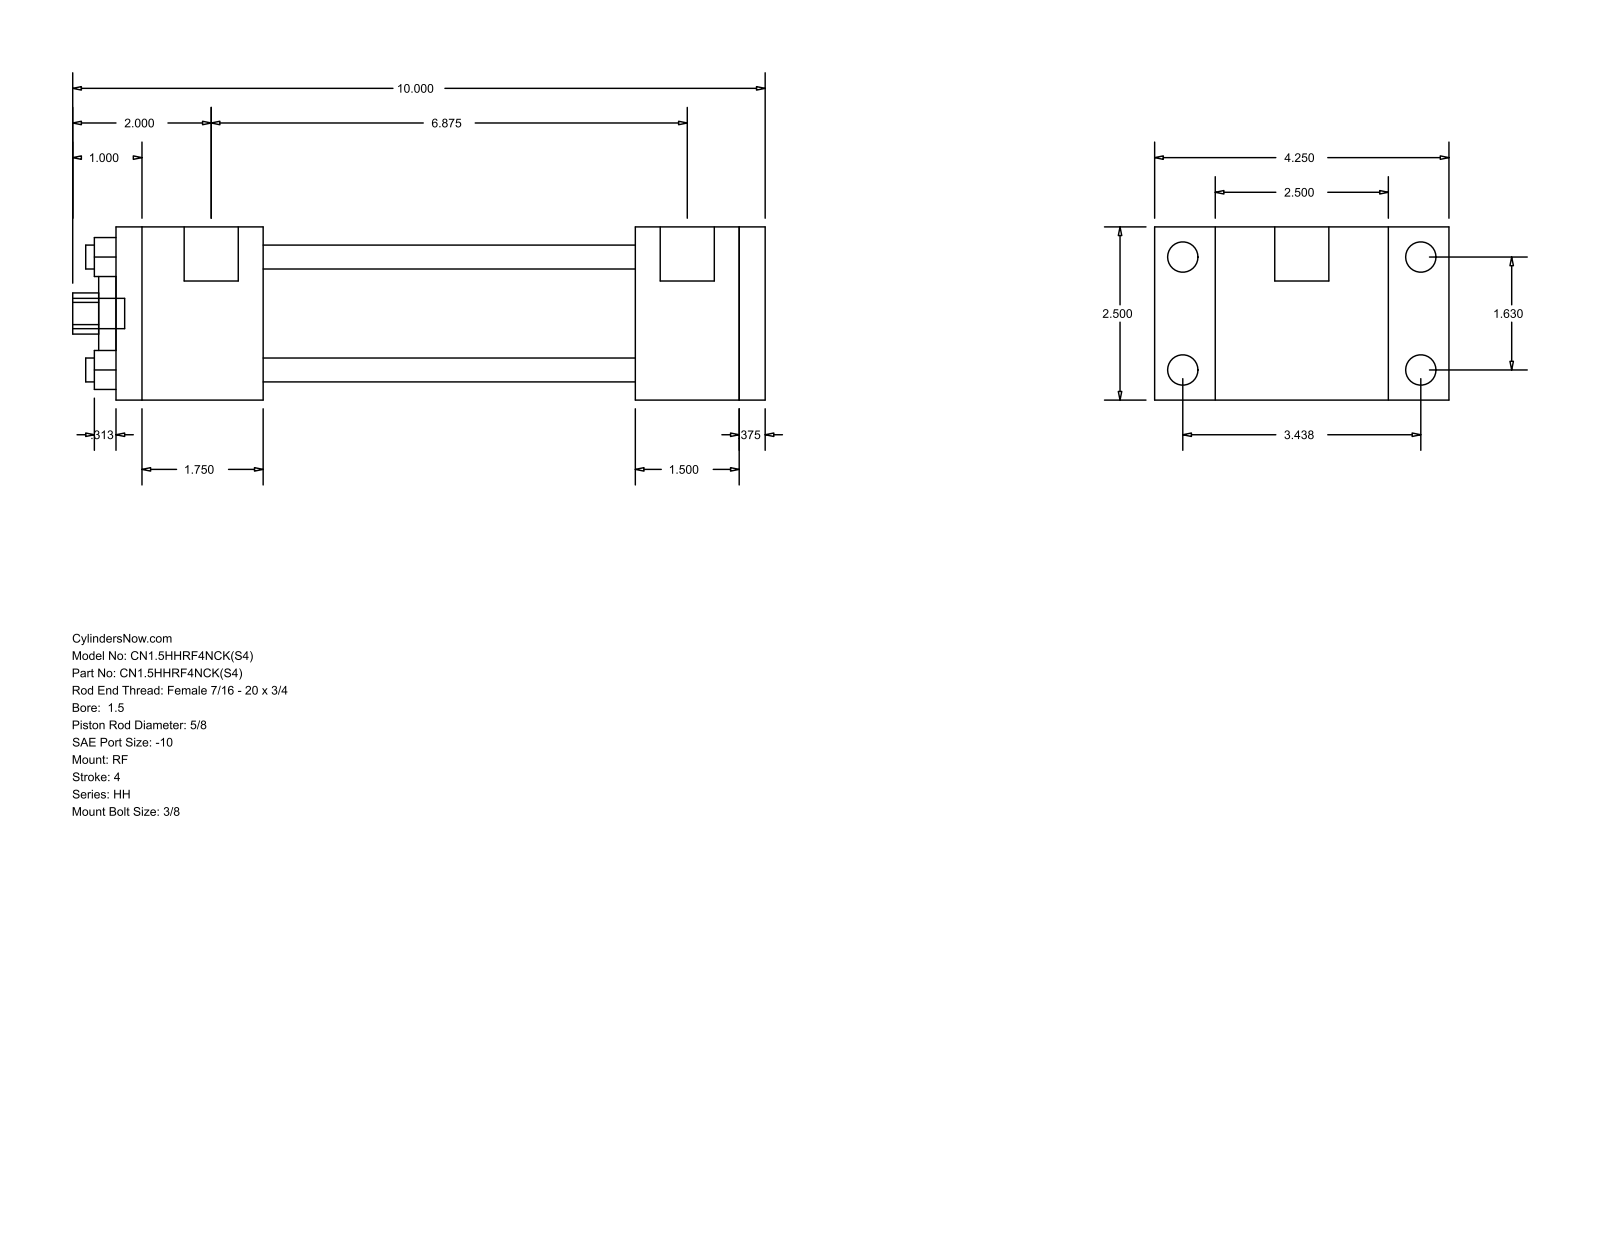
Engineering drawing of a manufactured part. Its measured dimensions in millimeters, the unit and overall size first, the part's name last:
Units: millimetres
Overall size (bounding box): 254 × 107.95 × 63.5
Round holes (diameter × count): ⌀8.76 ×4, ⌀15.88 ×1, ⌀28.57 ×1, ⌀44.45 ×1
Round bosses / shafts (diameter × count): ⌀11.13 ×4, ⌀5.56 ×4, ⌀19.84 ×2, ⌀11.11 ×1
Partial cylindrical surfaces — rounded edges, fillets, slot ends (radius × count): R7.54 ×1
Main face-to-face distances: 63.5, 238.12, 9.53, 228.59, 53.97, 190.5, 136.53, 174.62, 184.15, 38.09
Hole centre spacings: 29.27, 41.4, 58.55
Bodies: 0 solids, 92 faces (64 planar, 28 cylindrical, 0 other)
Part name (STEP PRODUCT): HH_RF__0150_0.625
STEP written by: GSSL Pune (CONFIG_CONTROL_DESIGN)
